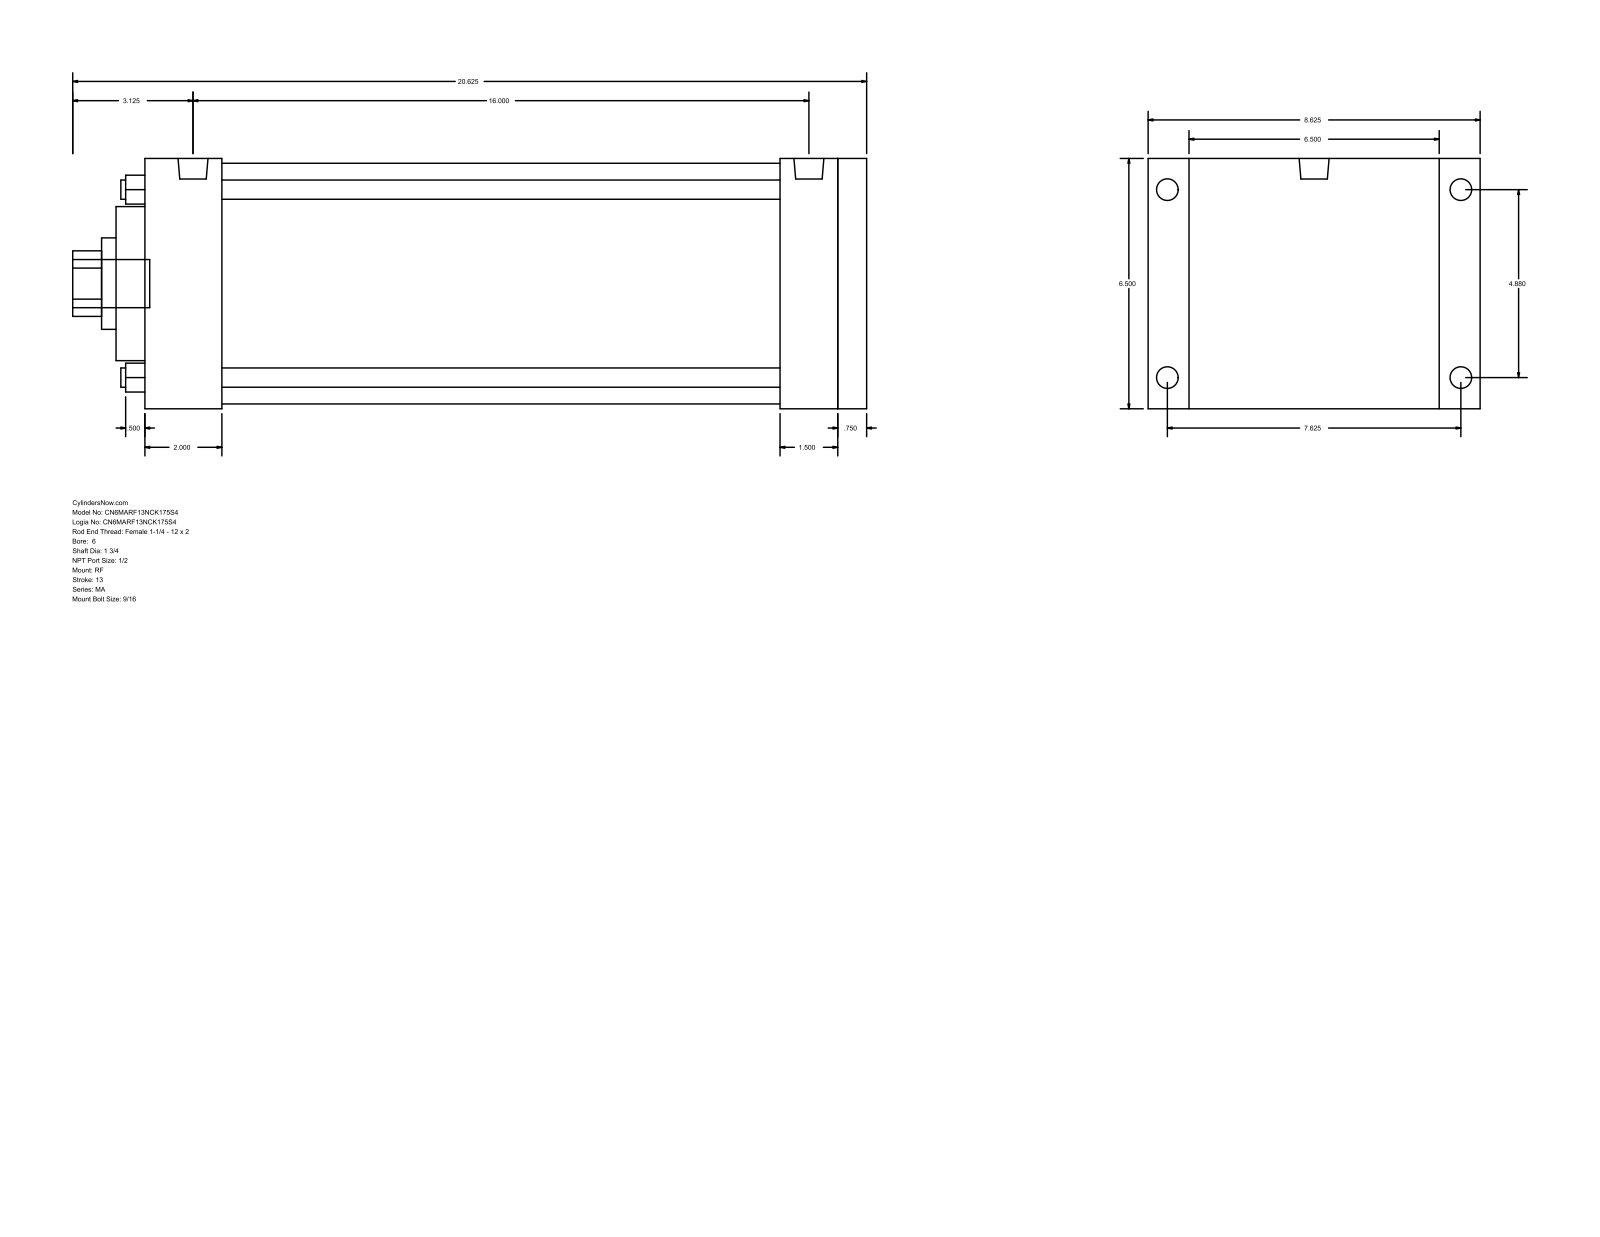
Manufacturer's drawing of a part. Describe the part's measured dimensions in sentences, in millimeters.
The part is named "MA_RF__0600_1.75". Its 3-D file was written by "GSSL Pune (CONFIG_CONTROL_DESIGN)". It is 0 solids with 94 faces: 65 planar, 29 cylindrical and 0 other. Overall it measures 523.88 by 219.07 by 165.1 millimeters. Round holes: 4 of diameter 12.7, 1 of diameter 44.45, 1 of diameter 60.33, 1 of diameter 101.6, 1 of diameter 158.75. Round bosses or shafts: 4 of diameter 17.46, 4 of diameter 14.29, 2 of diameter 19.77, 1 of diameter 31.75. Partial cylindrical surfaces (rounded edges, fillets, slot ends): 1 of radius 21.63. The main face-to-face distances are 165.1, 476.26, 457.2, 19.06, 19.05, 50.8, 406.4, 425.46, 419.11, 368.31. The hole center spacings are 87.65, 123.96, 175.31.
